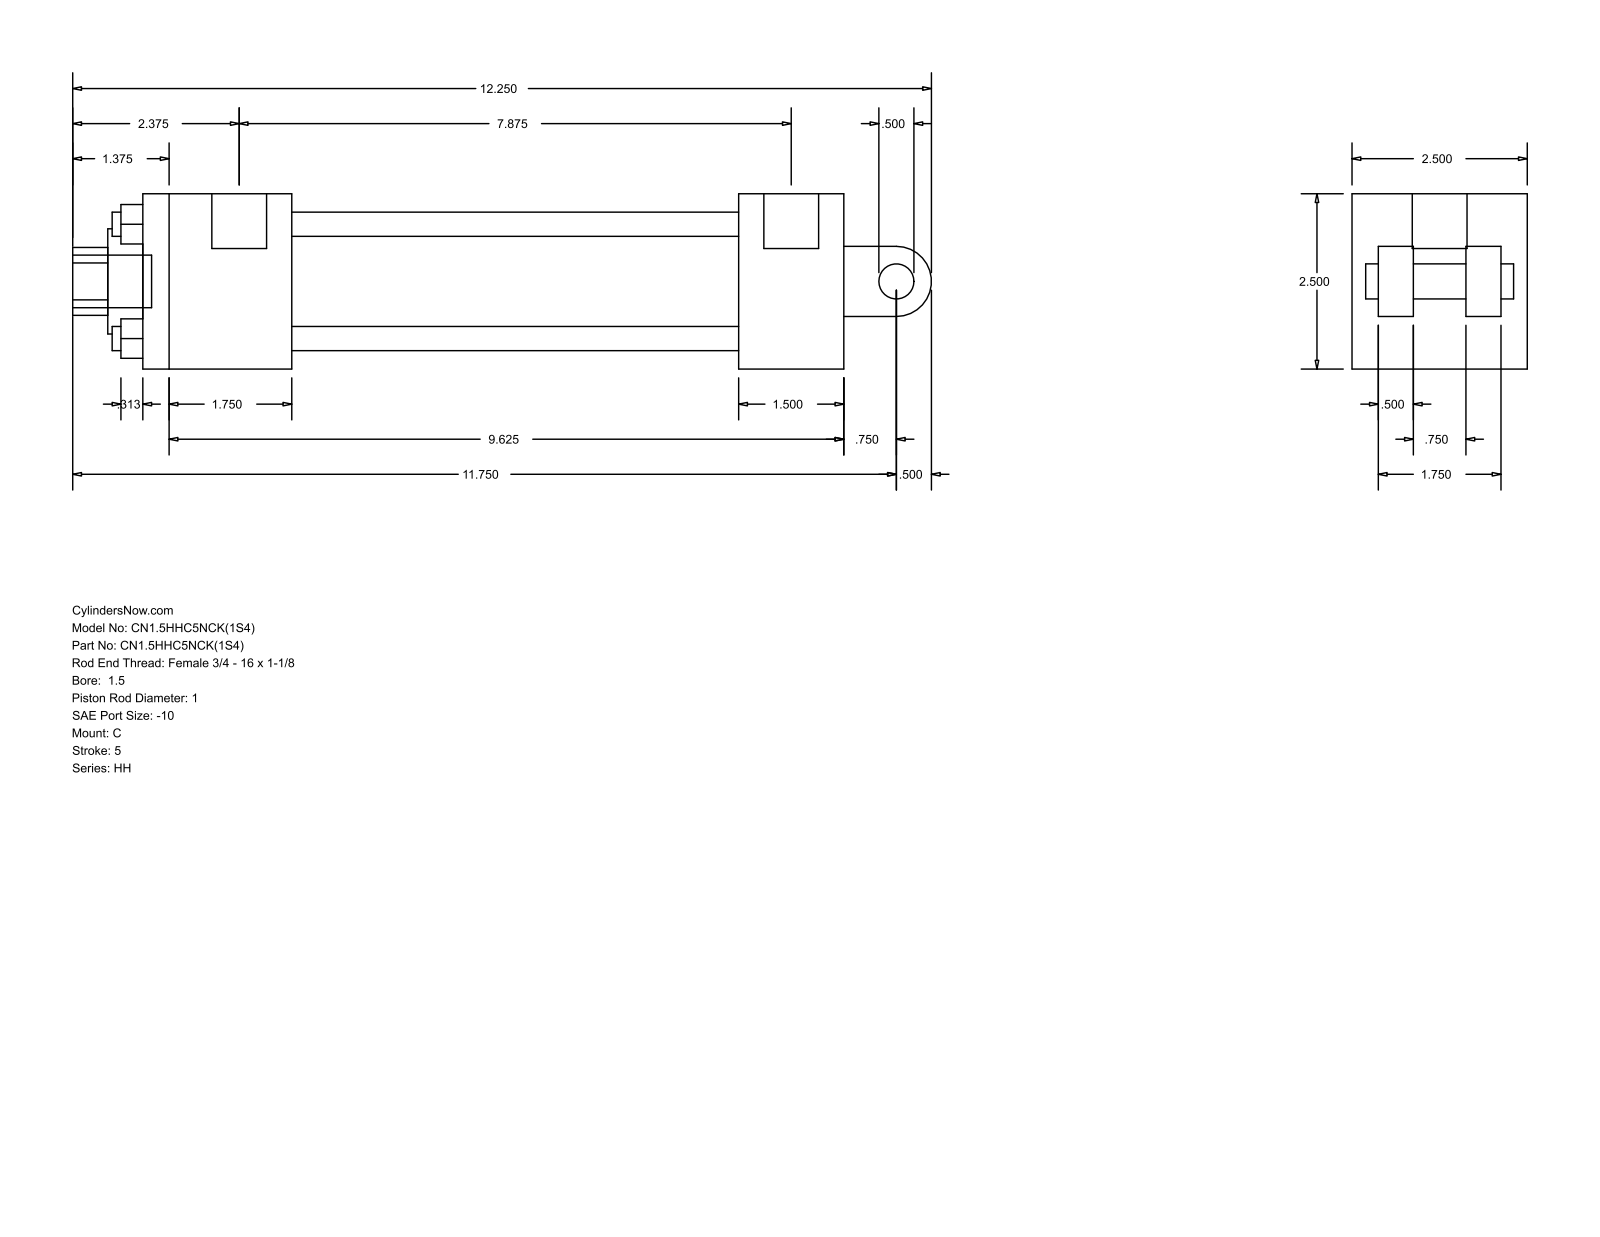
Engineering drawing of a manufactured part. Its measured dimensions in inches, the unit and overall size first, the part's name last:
Units: inches
Overall size (bounding box): 12.25 × 2.5 × 2.5
Round holes (diameter × count): ⌀0.345 ×4, ⌀0.219 ×2, ⌀0.781 ×1, ⌀1 ×1, ⌀1.5 ×1, ⌀1.75 ×1
Round bosses / shafts (diameter × count): ⌀0.219 ×2, ⌀0.781 ×1, ⌀0.75 ×1, ⌀0.5 ×1
Partial cylindrical surfaces — rounded edges, fillets, slot ends (radius × count): R0.484 ×1, R0.5 ×1
Main face-to-face distances: 2.5, 2.125, 6.375, 7.875, 1.5, 8.5, 10, 0.5, 0.875, 1.625
Hole centre spacings: 1.152, 1.63, 2.305, 0.063
Bodies: 0 solids, 99 faces (70 planar, 29 cylindrical, 0 other)
Part name (STEP PRODUCT): HH_C__0150_1
STEP written by: GSSL Pune (CONFIG_CONTROL_DESIGN)
